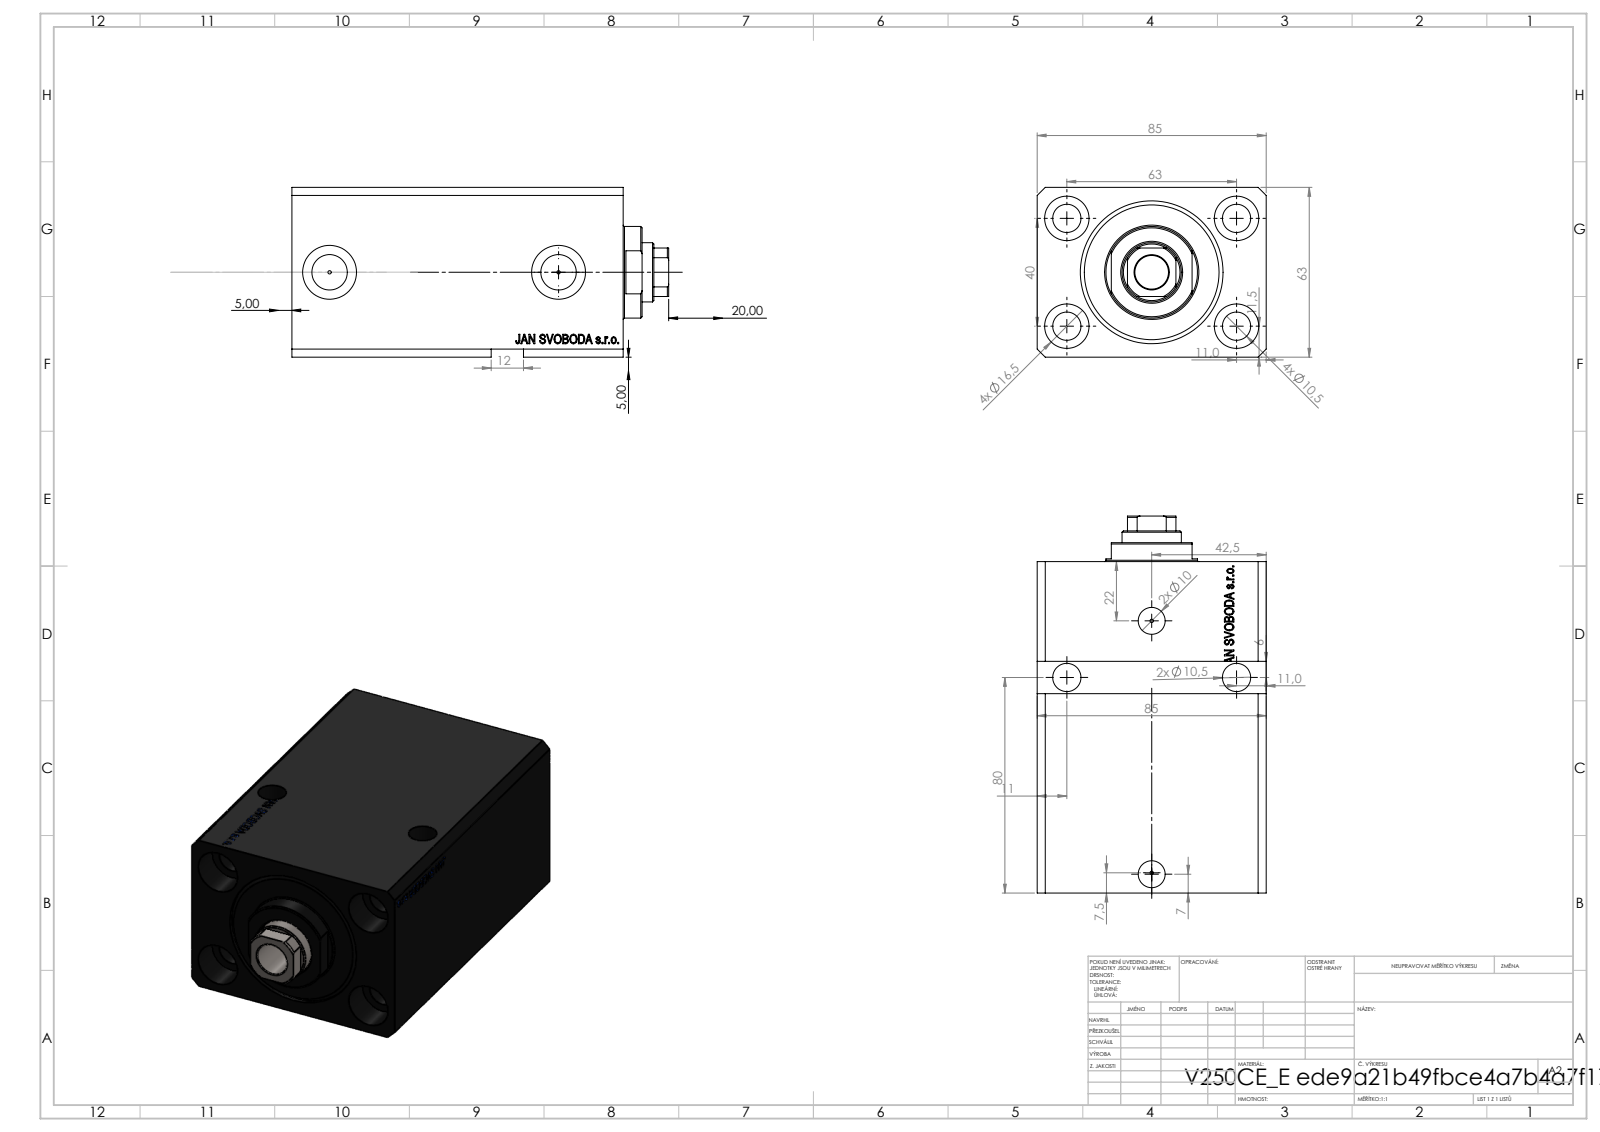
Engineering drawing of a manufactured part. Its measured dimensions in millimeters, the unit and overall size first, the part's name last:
Units: millimetres
Overall size (bounding box): 140 × 85 × 63
Round holes (diameter × count): ⌀10.5 ×8, ⌀1.25 ×4, ⌀16.5 ×4, ⌀10 ×2, ⌀13.16 ×2, ⌀20 ×2, ⌀12.5 ×1, ⌀22 ×1, ⌀40 ×1, ⌀53 ×1
Round bosses / shafts (diameter × count): ⌀34 ×1
Partial cylindrical surfaces — rounded edges, fillets, slot ends (radius × count): R10.5 ×1
Main face-to-face distances: 63, 85, 123, 17, 106, 11.4, 94.6, 111.6, 56, 11
Hole centre spacings: 37.31, 63, 37.86, 40, 41.8, 42.15, 45, 73.13
Volume: 118 599 mm³ · Surface area: 108 867 mm²
Bodies: 2 solids, 937 faces (459 planar, 104 cylindrical, 374 other)
Part name (STEP PRODUCT): V250CE_E_Body; V250CE_C_VCP; V250CE_VC_E
STEP written by: SolidWorks 2019 (CONFIG_CONTROL_DESIGN)
